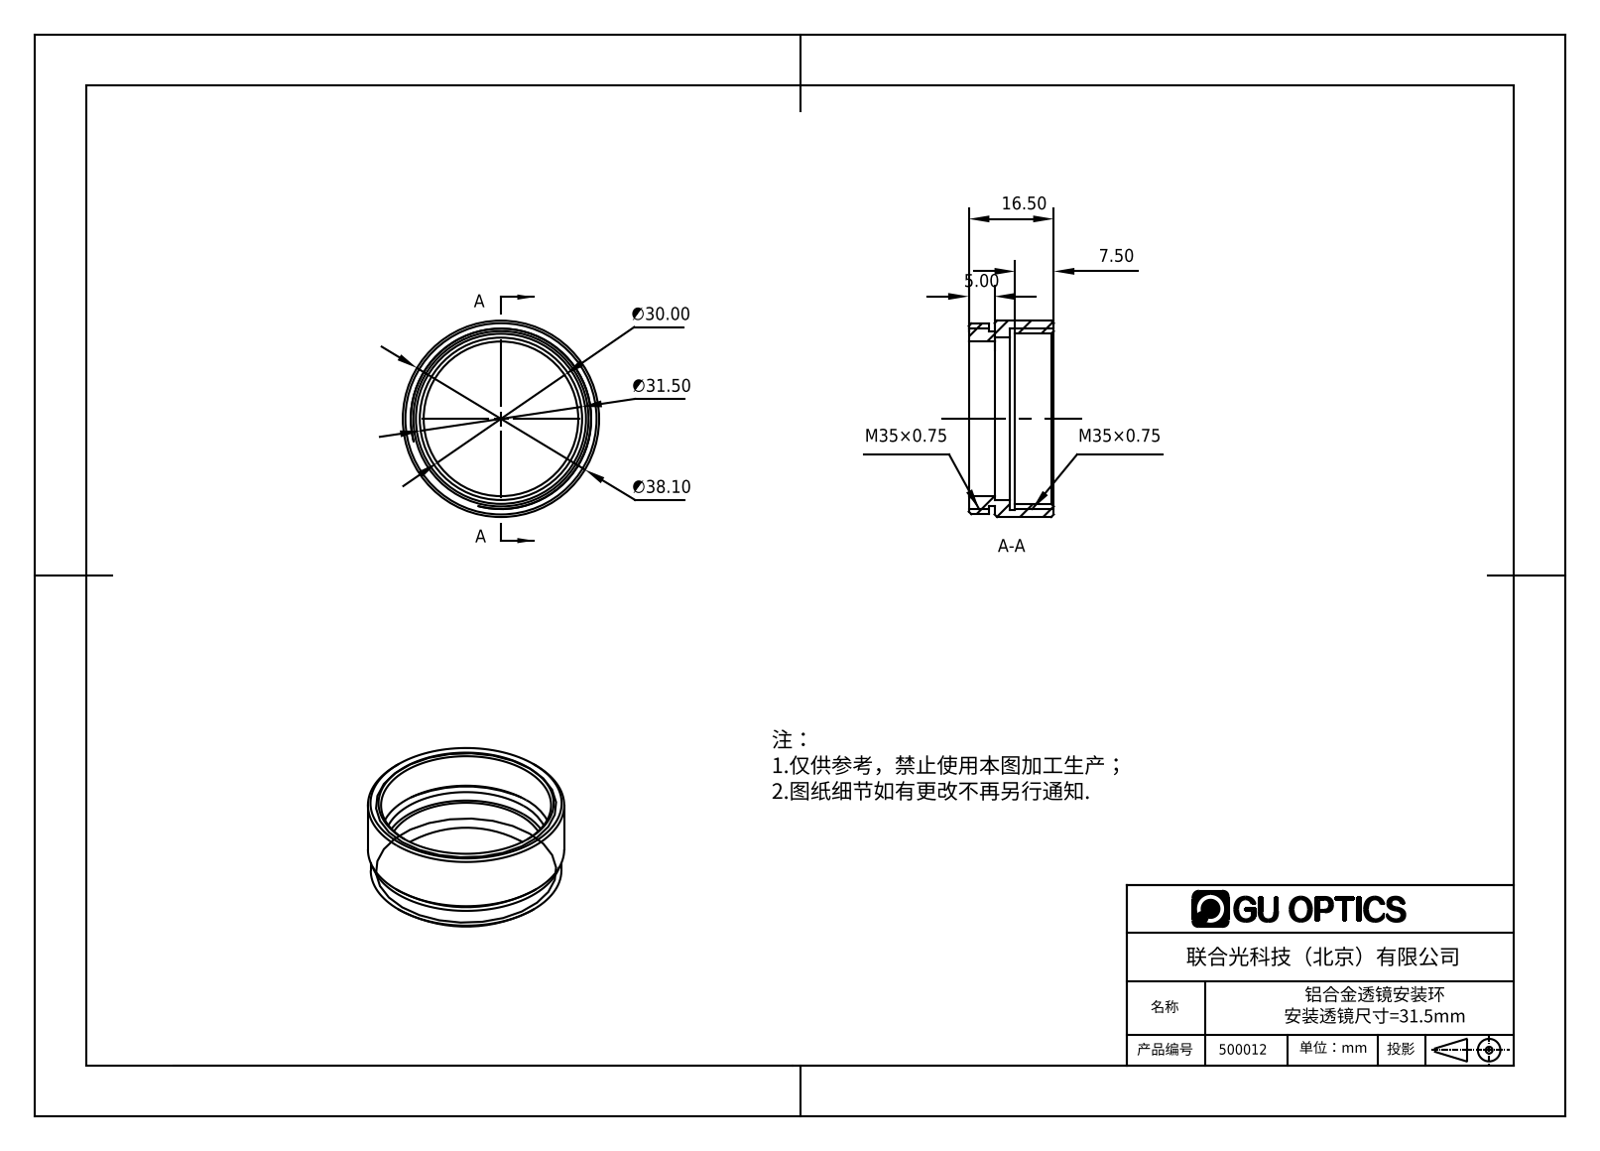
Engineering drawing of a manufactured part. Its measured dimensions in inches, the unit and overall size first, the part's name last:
Units: inches
Overall size (bounding box): 1.5 × 1.5 × 0.65
Round holes (diameter × count): ⌀1.181 ×1, ⌀1.24 ×1, ⌀1.299 ×1, ⌀1.386 ×1
Round bosses / shafts (diameter × count): ⌀1.5 ×1, ⌀1.457 ×1, ⌀1.339 ×1
Main face-to-face distances: 0.157, 0.039, 0.118, 0.197, 0.276, 0.079, 0.65, 0.453, 0.374, 0.492
Volume: 0.301 in³ · Surface area: 7.612 in²
Bodies: 1 solid, 29 faces (7 planar, 14 cylindrical, 8 other)
Part name (STEP PRODUCT): 500012
STEP written by: SolidWorks 2016 (AUTOMOTIVE_DESIGN)
